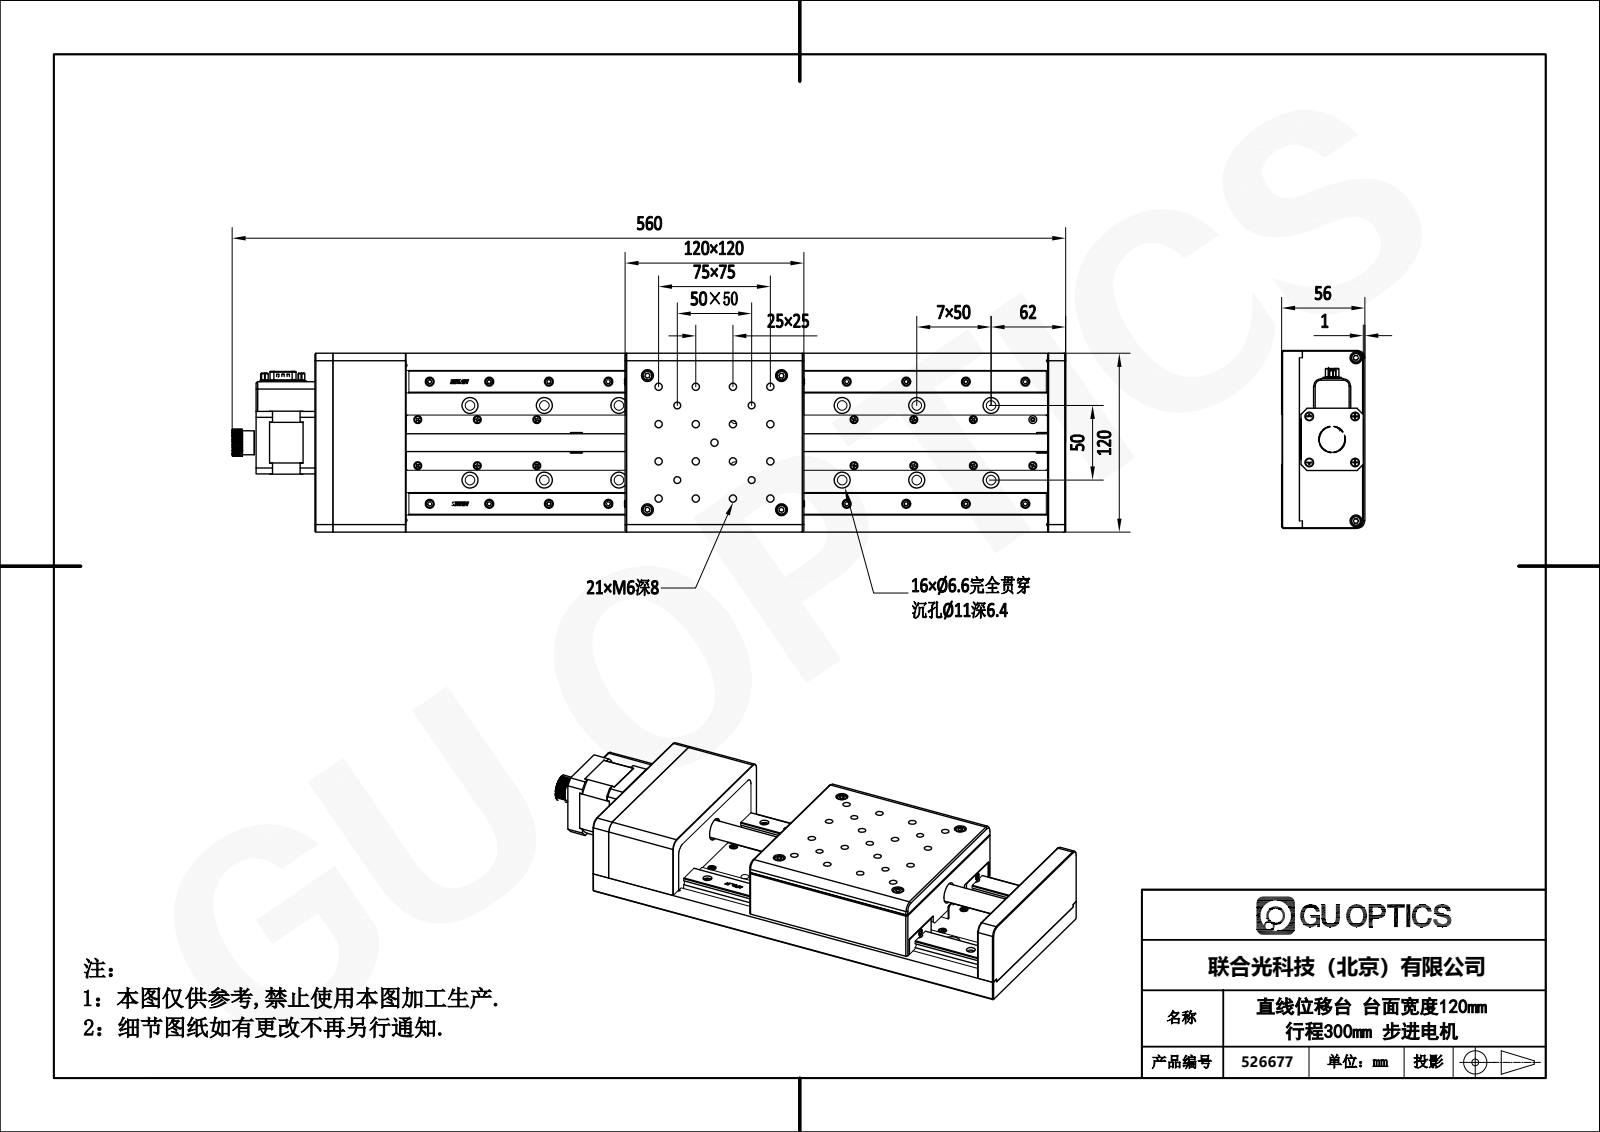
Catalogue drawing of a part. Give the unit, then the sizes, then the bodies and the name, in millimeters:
Units: millimetres
Overall size (bounding box): 559.6 × 120 × 56
Round holes (diameter × count): ⌀6 ×20, ⌀5 ×17, ⌀6.6 ×16, ⌀8 ×14, ⌀11 ×12, ⌀2 ×5, ⌀4.71 ×4, ⌀2.5 ×2, ⌀4.5 ×2, ⌀3 ×1, ⌀3.3 ×1, ⌀14 ×1
Round bosses / shafts (diameter × count): ⌀4.4 ×15, ⌀1 ×9, ⌀7 ×4, ⌀5.5 ×4, ⌀4.2 ×2, ⌀12 ×1
Partial cylindrical surfaces — rounded edges, fillets, slot ends (radius × count): R0.5 ×20, R0.3 ×10, R1 ×8, R0.4 ×6, R5 ×6, R1.5 ×4, R9 ×1, R20.5 ×1
Main face-to-face distances: 14, 34, 8, 13.7, 28, 120, 13.8, 13.5, 42, 42.2
Hole centre spacings: 50, 70.71, 100, 111.8, 150, 158.11, 200, 206.16
Bodies: 0 solids, 1263 faces (628 planar, 400 cylindrical, 235 other)
Part name (STEP PRODUCT): FMS120-300
STEP written by: SolidWorks 2017 (CONFIG_CONTROL_DESIGN)
